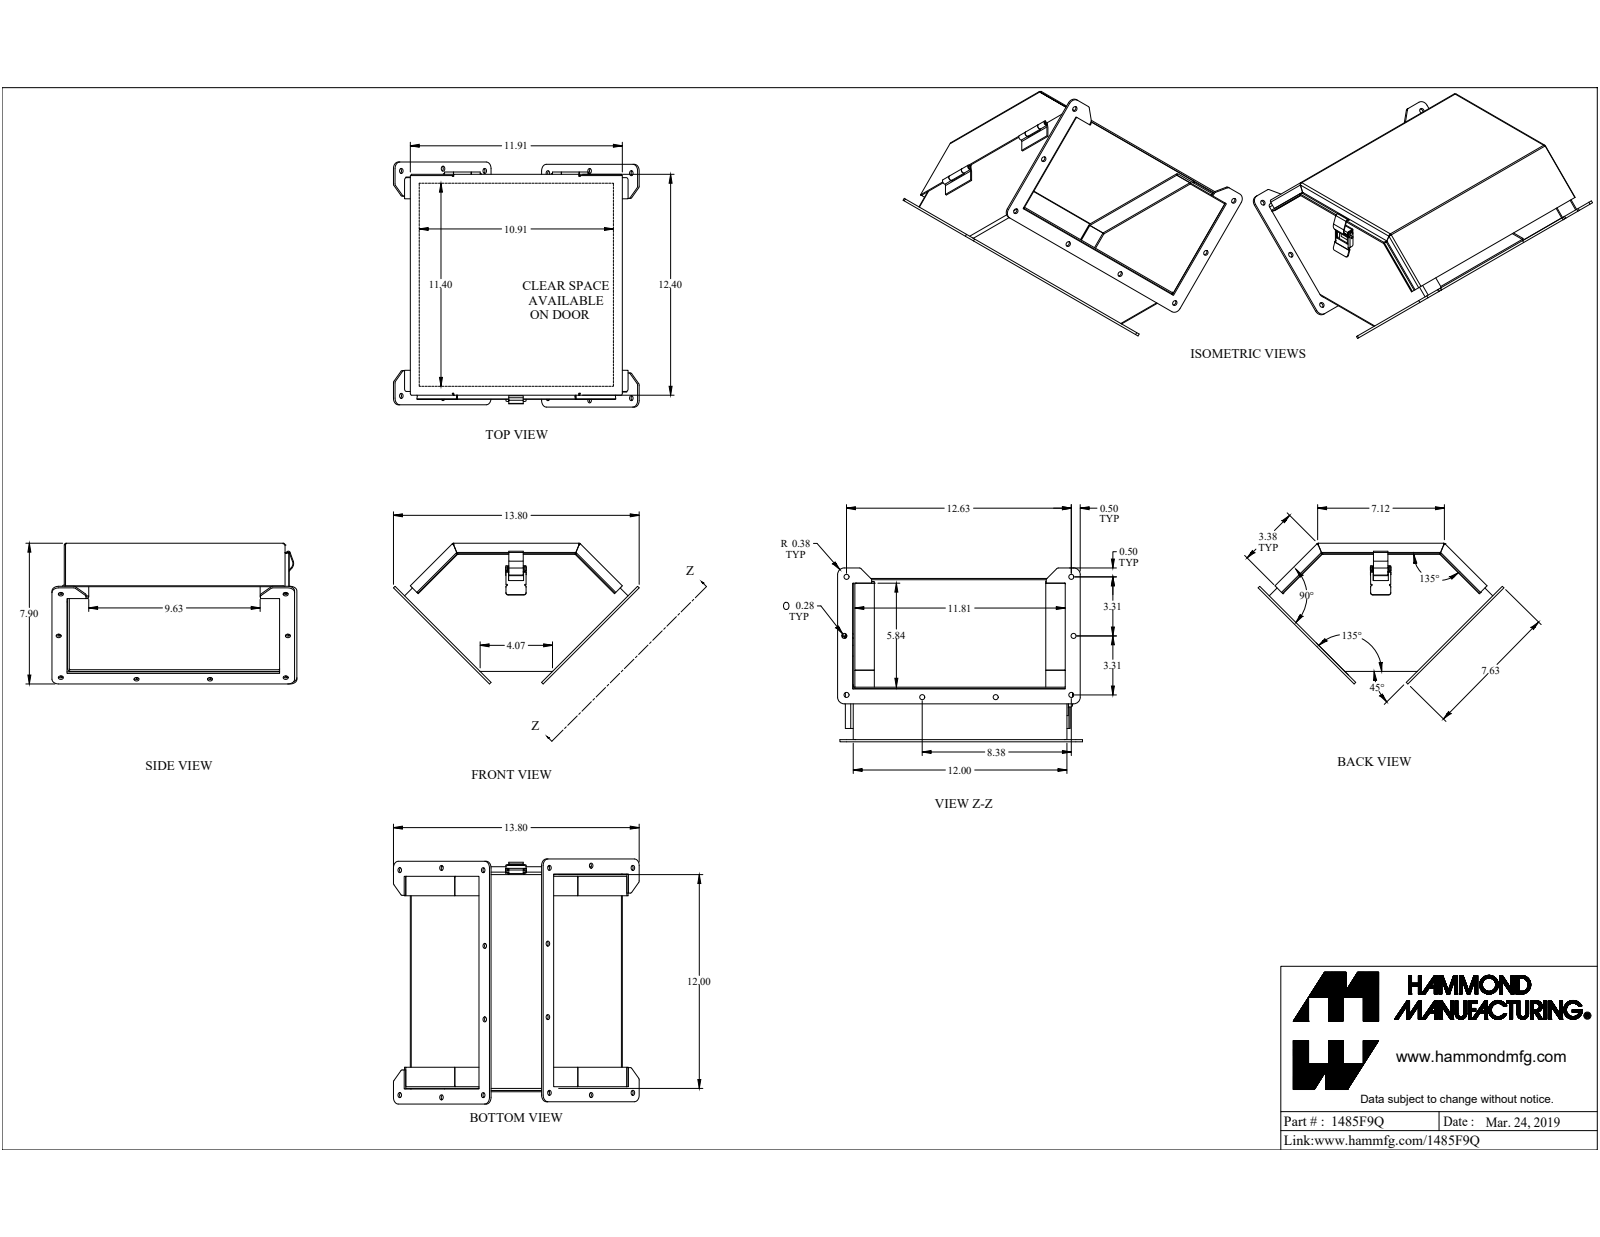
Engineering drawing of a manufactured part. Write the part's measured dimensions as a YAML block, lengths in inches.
part_name: "1485F9Q"
step_written_by: "SolidWorks 2019 (CONFIG_CONTROL_DESIGN)"
units: inches
bodies: {solids: 13, faces: 380, planar: 228, cylindrical: 132, other: 20}
overall_size: [13.799, 13.754, 7.899]
volume: 40.62
surface_area: 964.2
round_holes:
  - {diameter: 0.281, count: 16}
  - {diameter: 0.125, count: 1}
  - {diameter: 0.13, count: 1}
  - {diameter: 0.164, count: 1}
round_bosses_or_shafts:
  - {diameter: 0.187, count: 2}
  - {diameter: 0.275, count: 1}
  - {diameter: 0.156, count: 1}
  - {diameter: 0.125, count: 1}
partial_cylinders:
  - {radius: 0.125, count: 11}
  - {radius: 0.036, count: 9}
  - {radius: 0.108, count: 9}
  - {radius: 0.048, count: 8}
  - {radius: 0.143, count: 8}
  - {radius: 0.375, count: 8}
  - {radius: 0.016, count: 7}
  - {radius: 0.035, count: 3}
face_to_face_distances: [0.072, 0.095, 11.905, 11.81, 12, 8.971, 9.043, 7.03, 7.102, 7.125]
hole_center_spacings: [3.315, 13.173, 4.252, 5.564, 6.625, 7.977, 8.376, 9.169]
